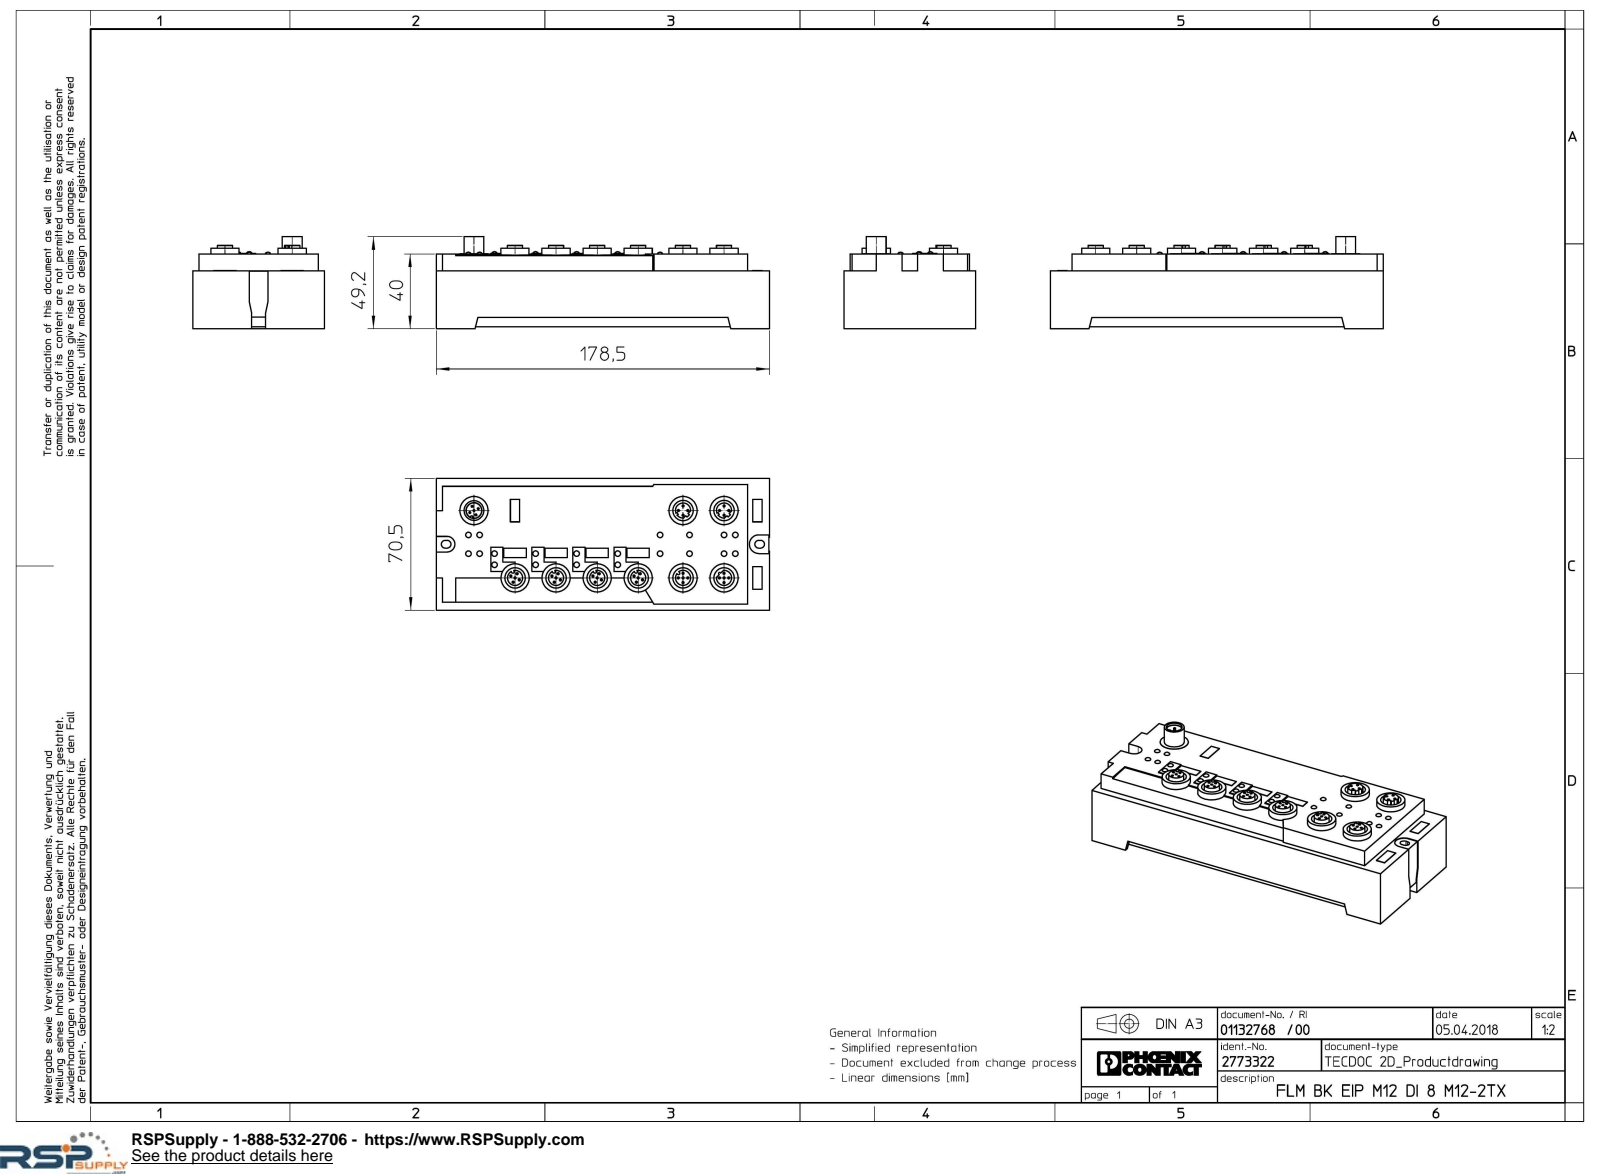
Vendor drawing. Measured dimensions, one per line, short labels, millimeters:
name: FLM_BK...M12_DI_8_M12_2TX-select
written by: Creo Elements/Direct Modeling 20.1A 29-Sep-2018 (C) Parametric Technology GmbH (AUTOMOTIVE_DESIGN)
unit: mm
bodies: 1 solid, 414 faces (223 planar, 151 cylindrical, 40 other)
size: 178.5 × 70.5 × 49.25
volume: 464 732 mm³; area: 52 333 mm²
holes: 38× ⌀1.1, 8× ⌀10.92, 1× ⌀8.3, 1× ⌀8.5
bosses: 9× ⌀15.1, 5× ⌀8.1, 5× ⌀1, 1× ⌀10.6
rounds: 5× R0.75, 4× R2.1, 2× R0.6, 2× R4.06, 1× R4.05, 1× R4.2, 1× R5, 1× R200
face distances: 39, 70.5, 9, 1, 30, 4.25, 66.25, 178.5, 0.7, 4.95
hole spacings: 3.54, 22, 2.5, 5, 2.51, 36.09, 36, 3.53
